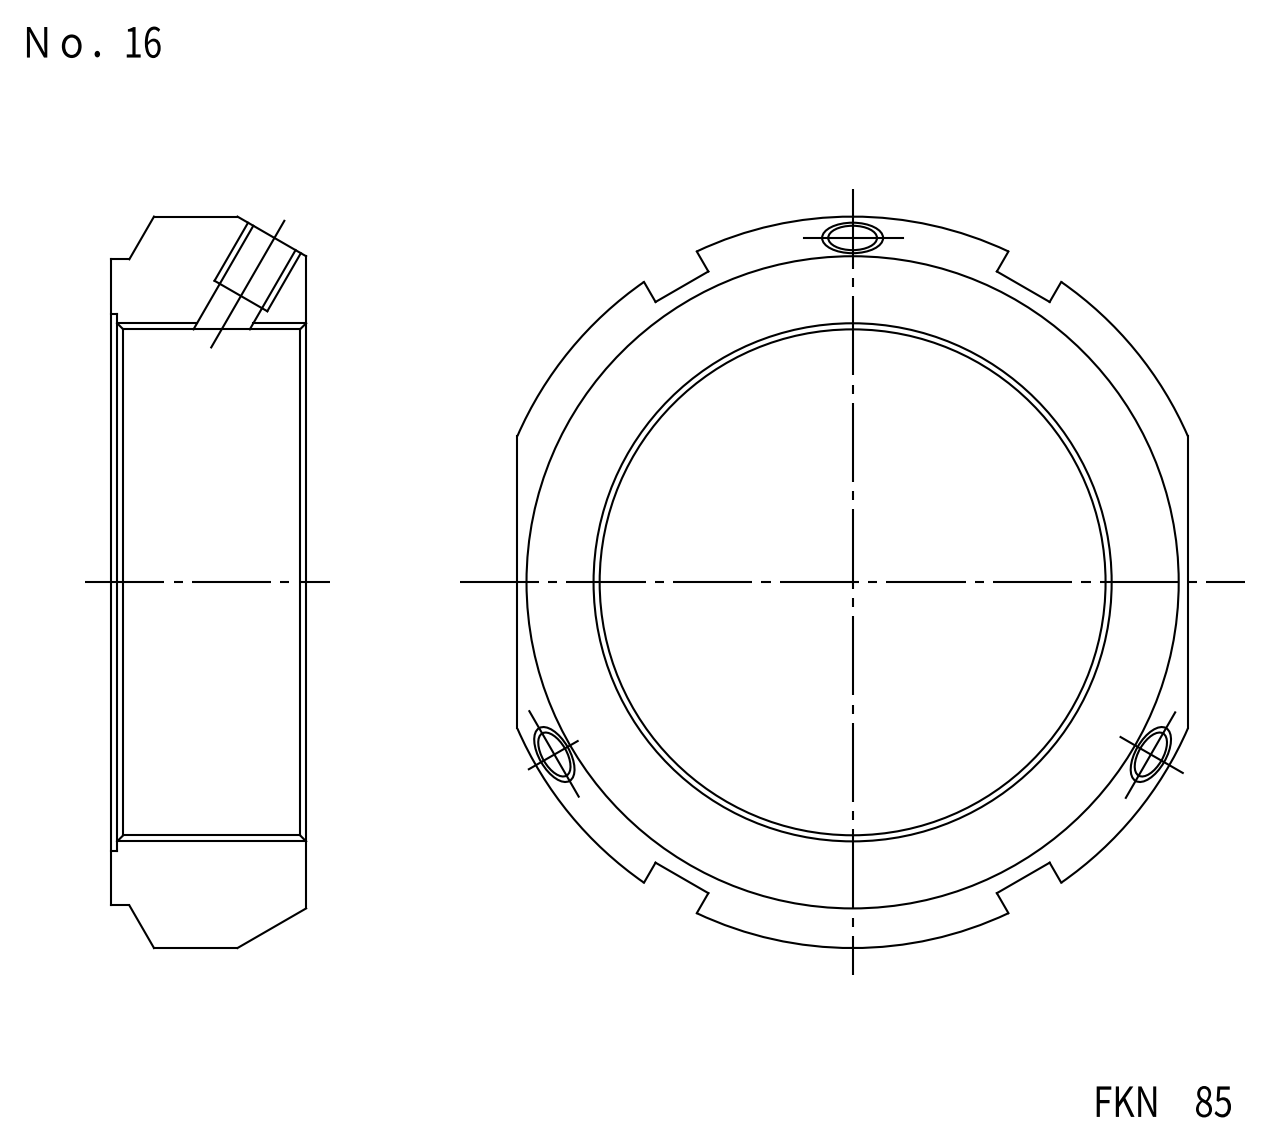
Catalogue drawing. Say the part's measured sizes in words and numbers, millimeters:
The part is named "FKD FKN85". Its 3-D file was written by "Autodesk Inventor LT (CONFIG_CONTROL_DESIGN)". It is 1 solid with 37 faces: 20 planar, 15 cylindrical and 2 other. Overall it measures 120 by 110 by 32 millimeters. Its volume is 142 395 cubic millimeters and its surface area 29 709 square millimeters. Round holes: 3 of diameter 8.38, 3 of diameter 10.2, 1 of diameter 85, 1 of diameter 88. Round bosses or shafts: 1 of diameter 106. Partial cylindrical surfaces (rounded edges, fillets, slot ends): 1 of radius 60. The main face-to-face distances are 32, 110, 112, 1.5, 30.5, 10.
